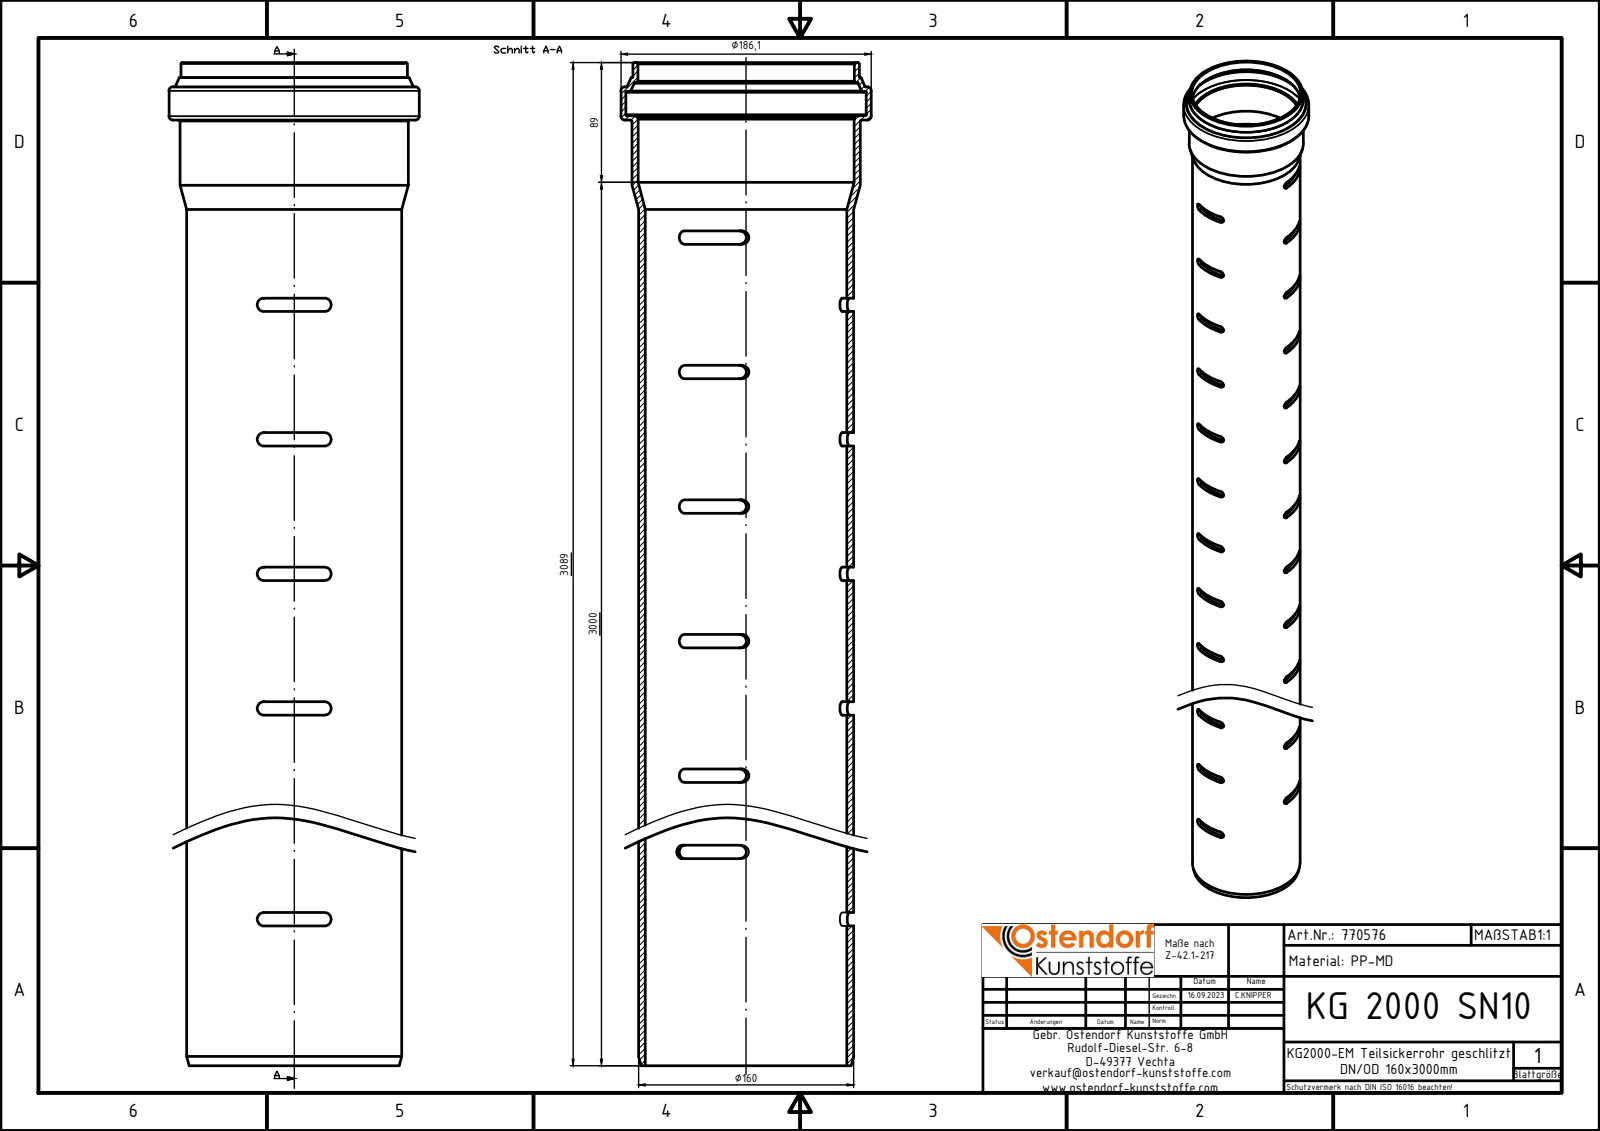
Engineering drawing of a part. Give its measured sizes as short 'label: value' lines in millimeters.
name: 770576z
written by: Autodesk Inventor 2024 (AUTOMOTIVE_DESIGN)
unit: mm
bodies: 1 solid, 385 faces (180 planar, 183 cylindrical, 22 other)
size: 3089 × 186.1 × 186.1
volume: 7 388 000 mm³; area: 2 994 000 mm²
holes: 1× ⌀149.85, 1× ⌀160.6, 1× ⌀161, 1× ⌀178.7
bosses: 1× ⌀186.1, 1× ⌀169.6, 1× ⌀168.4, 1× ⌀160
rounds: 174× R5
face distances: 100, 200, 300, 400, 500, 600, 700, 800, 900, 1000
